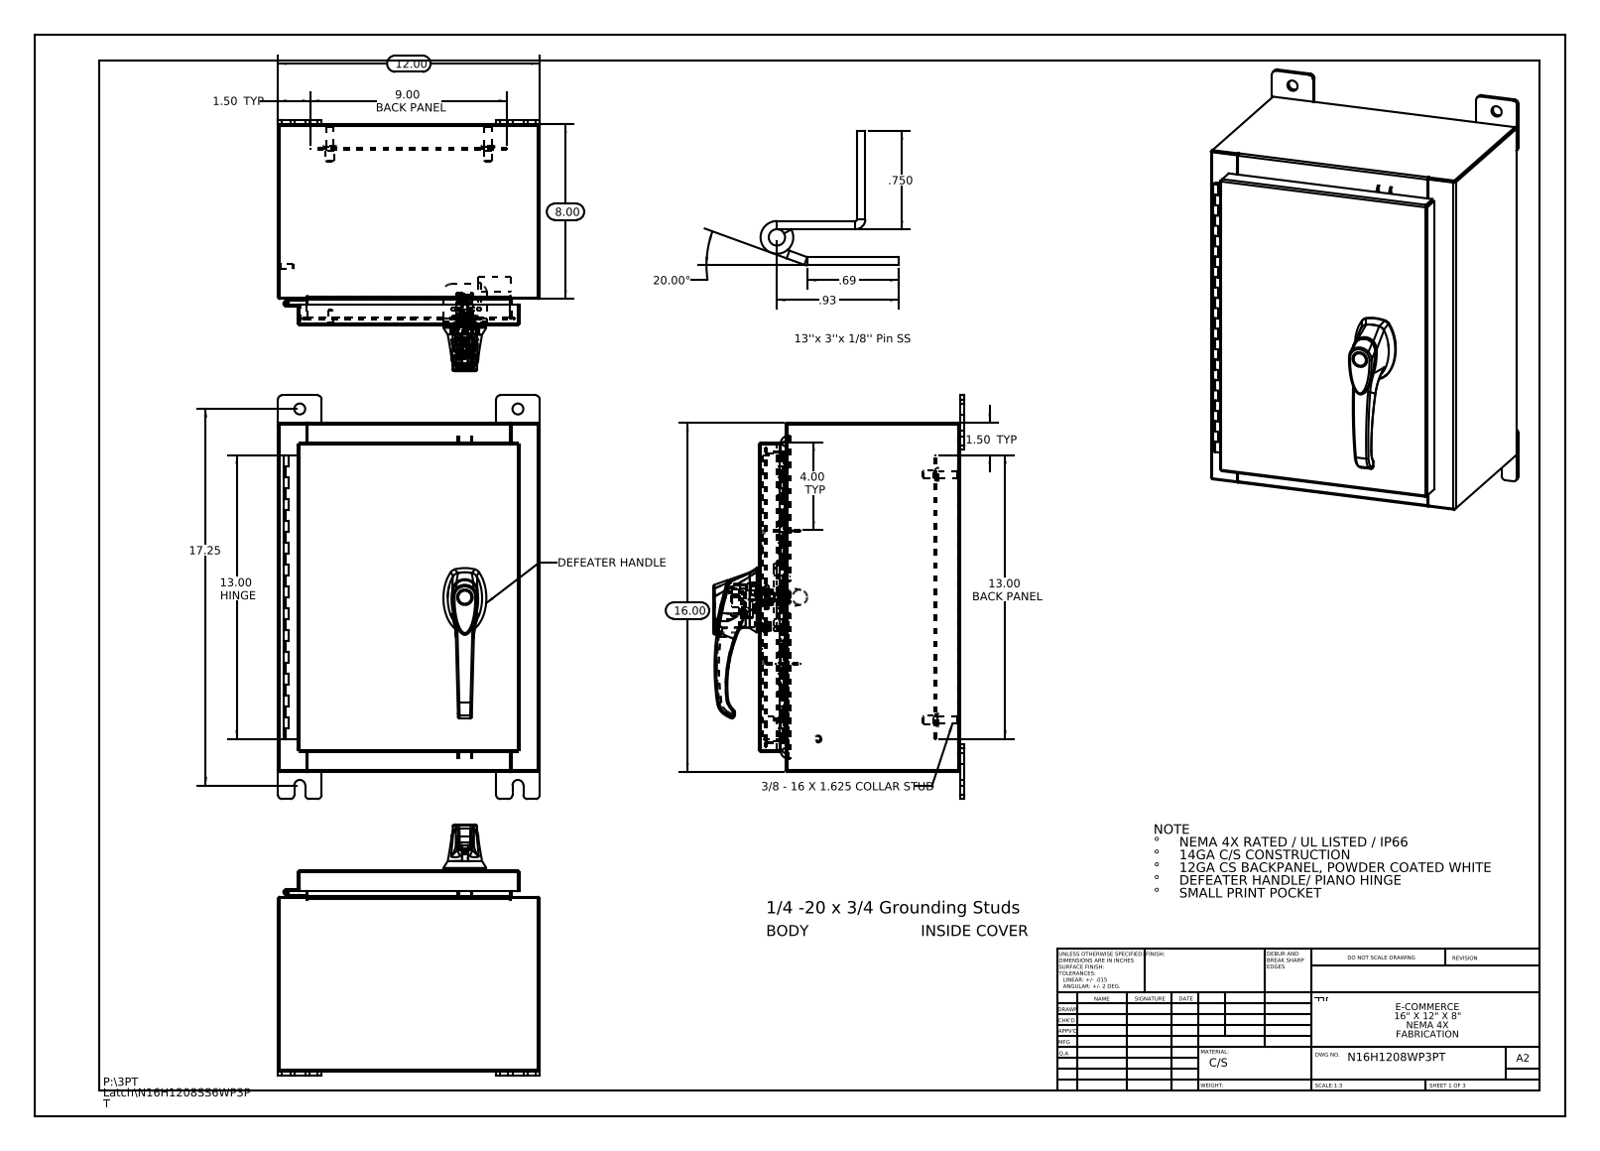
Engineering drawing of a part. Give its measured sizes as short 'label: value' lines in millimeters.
name: 00005090; 26161102; 297026; 297025 (+8 more)
written by: SolidWorks 2013 (CONFIG_CONTROL_DESIGN)
unit: mm
bodies: 31 solids, 2204 faces (757 planar, 793 cylindrical, 654 other)
size: 469.9 × 304.8 × 292
volume: 1 592 000 mm³; area: 1 543 000 mm²
holes: 8× ⌀12.7, 4× ⌀6.4, 3× ⌀3.5, 3× ⌀4.1, 2× ⌀2, 2× ⌀5.2, 2× ⌀8, 2× ⌀11.1, 1× ⌀3.2, 1× ⌀3.2, 1× ⌀5, 1× ⌀7
bosses: 4× ⌀15.9, 4× ⌀9.5, 4× ⌀8.4, 1× ⌀30, 1× ⌀19, 1× ⌀17.3, 1× ⌀16.8, 1× ⌀16.2
rounds: 37× R3, 33× R0.2, 24× R4.8, 20× R0.3, 18× R2.2, 15× R1, 12× R0.7, 6× R0.2
face distances: 1.9, 231.8, 302.9, 404.5, 229.9, 233.7, 201.3, 30.5, 301, 304.8
hole spacings: 94.2, 7.5, 15.9, 21.4, 31.8, 33.4, 33.5, 37.7
